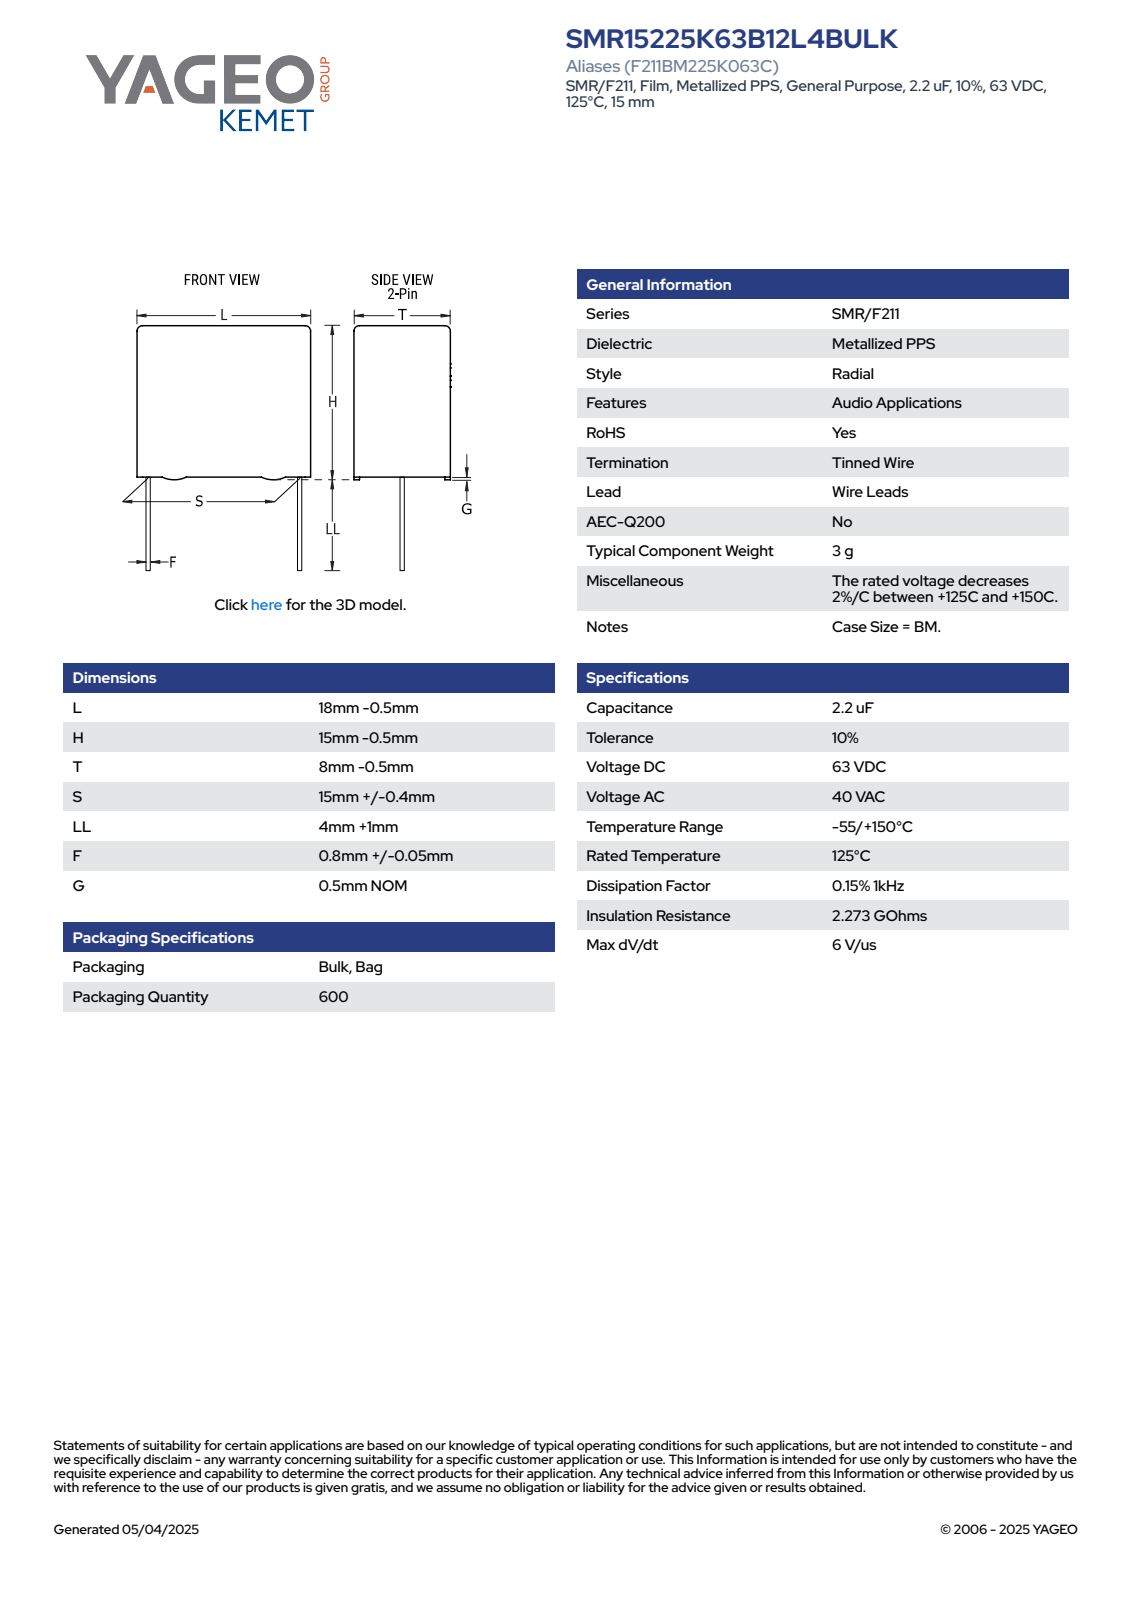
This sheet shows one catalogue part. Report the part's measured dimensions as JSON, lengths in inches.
{"part_name": "CFR_RBG_18X15X8_L17.5H14.5T7.5S15LL5F0.85G0.5", "step_written_by": "SolidWorks 2021 (AUTOMOTIVE_DESIGN)", "units": "inches", "bodies": {"solids": 4, "faces": 89, "planar": 81, "cylindrical": 8, "other": 0}, "overall_size": [0.768, 0.689, 0.295], "volume_in3": 0.113, "surface_area_in2": 1.592, "round_bosses_or_shafts": [[0.033, 2]], "partial_cylinders_radius": [[0.02, 4]], "face_to_face_distances": [0.295, 0.551, 0.689, 0.017, 0.278, 0.02, 0.571, 0.261, 0.197, 0.217]}
